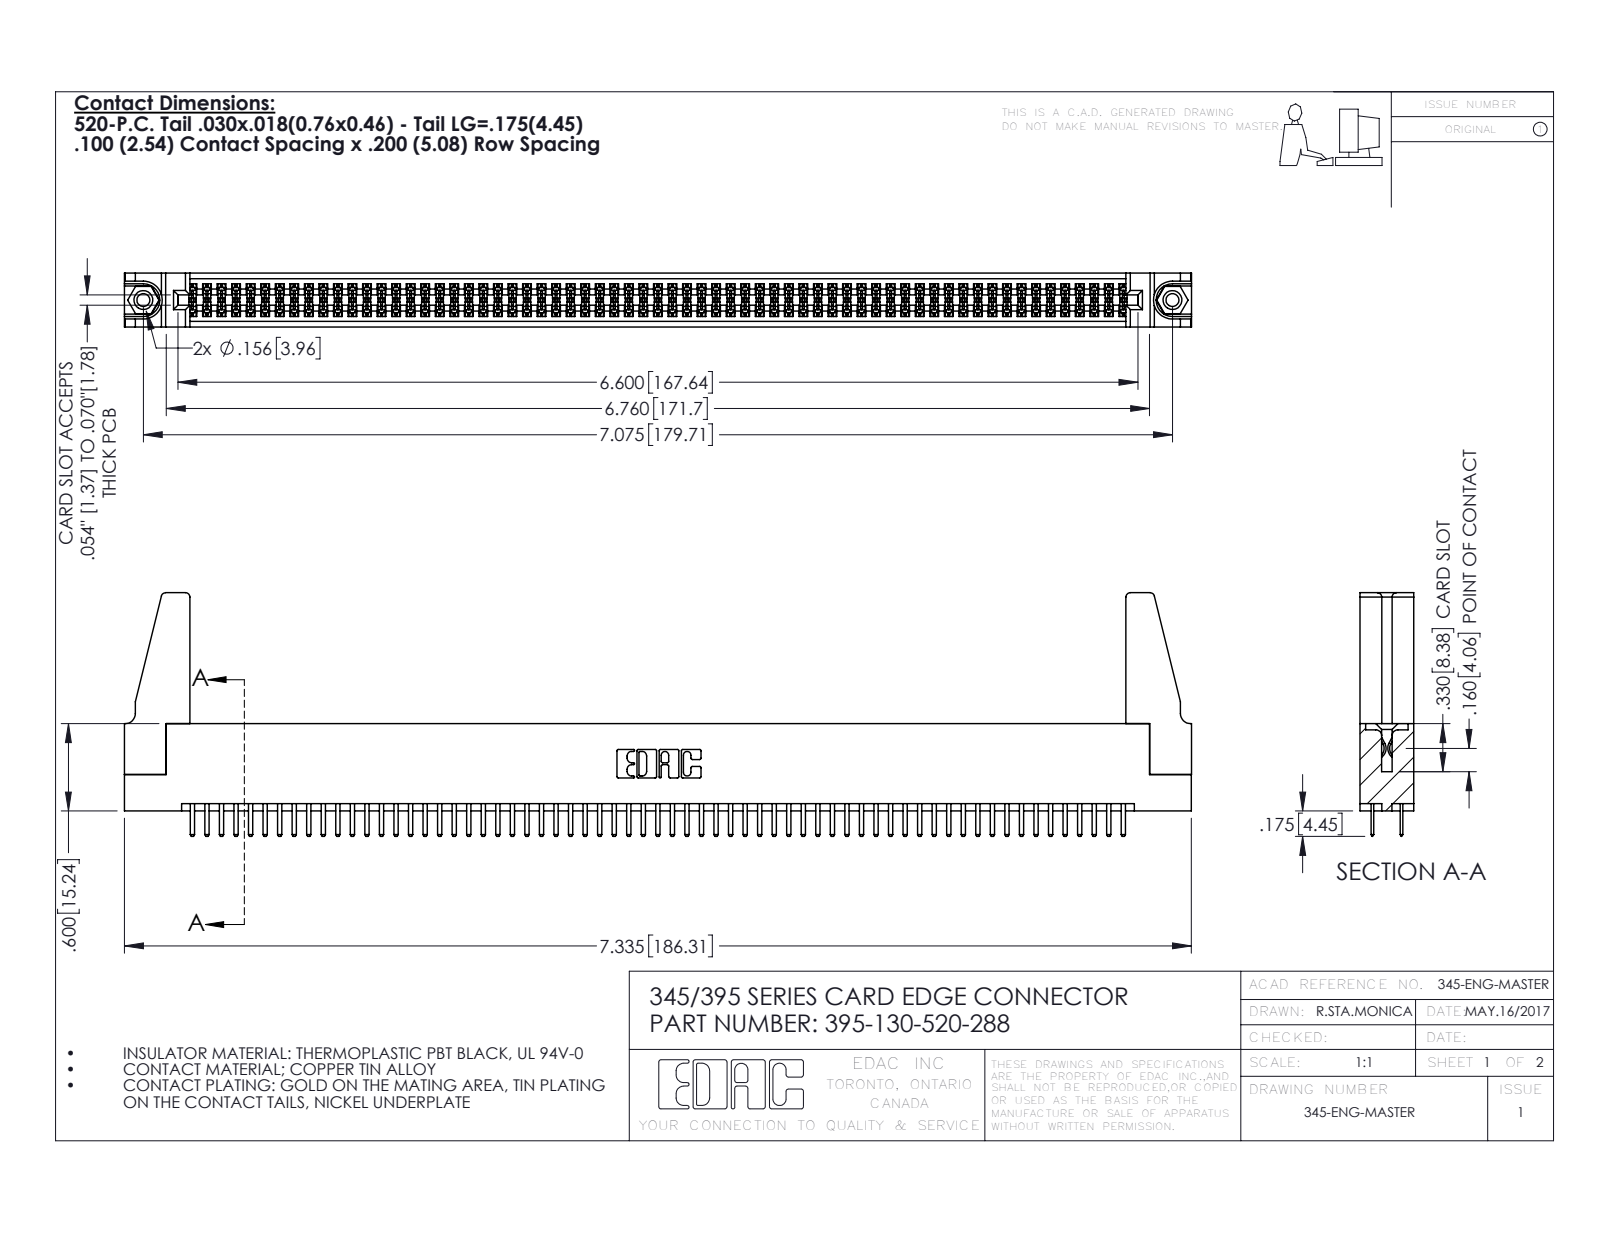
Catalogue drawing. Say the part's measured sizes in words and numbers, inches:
The part is named "345 Part_Flush Mounting Lugs - 0.156 Dia-TH; 395-130-520-288; 345-250-001_345-250-001-102; 345-220-078_345-220-088 (+1 more)". Its 3-D file was written by "SolidWorks 2016 (CONFIG_CONTROL_DESIGN)". It is 135 solids with 7270 faces: 4702 planar, 2552 cylindrical and 16 other. Overall it measures 7.336 by 1.675 by 0.37 inches. Its volume is 1.313 cubic inches and its surface area 47.17 square inches. Round holes: 2 of diameter 0.089, 2 of diameter 0.125, 2 of diameter 0.156, 1 of diameter 0.064. Round bosses or shafts: 2 of diameter 0.155. Partial cylindrical surfaces (rounded edges, fillets, slot ends): 195 of radius 0.006, 134 of radius 0.01, 22 of radius 0.01, 8 of radius 0.03, 6 of radius 0.007, 6 of radius 0.031, 3 of radius 0.026, 2 of radius 0.014. The main face-to-face distances are 0.072, 0.298, 0.37, 0.2, 0.098, 0.272, 0.025, 0.225, 0.022, 0.072. The hole center spacings are 0.27, 6.839, 7.075.
